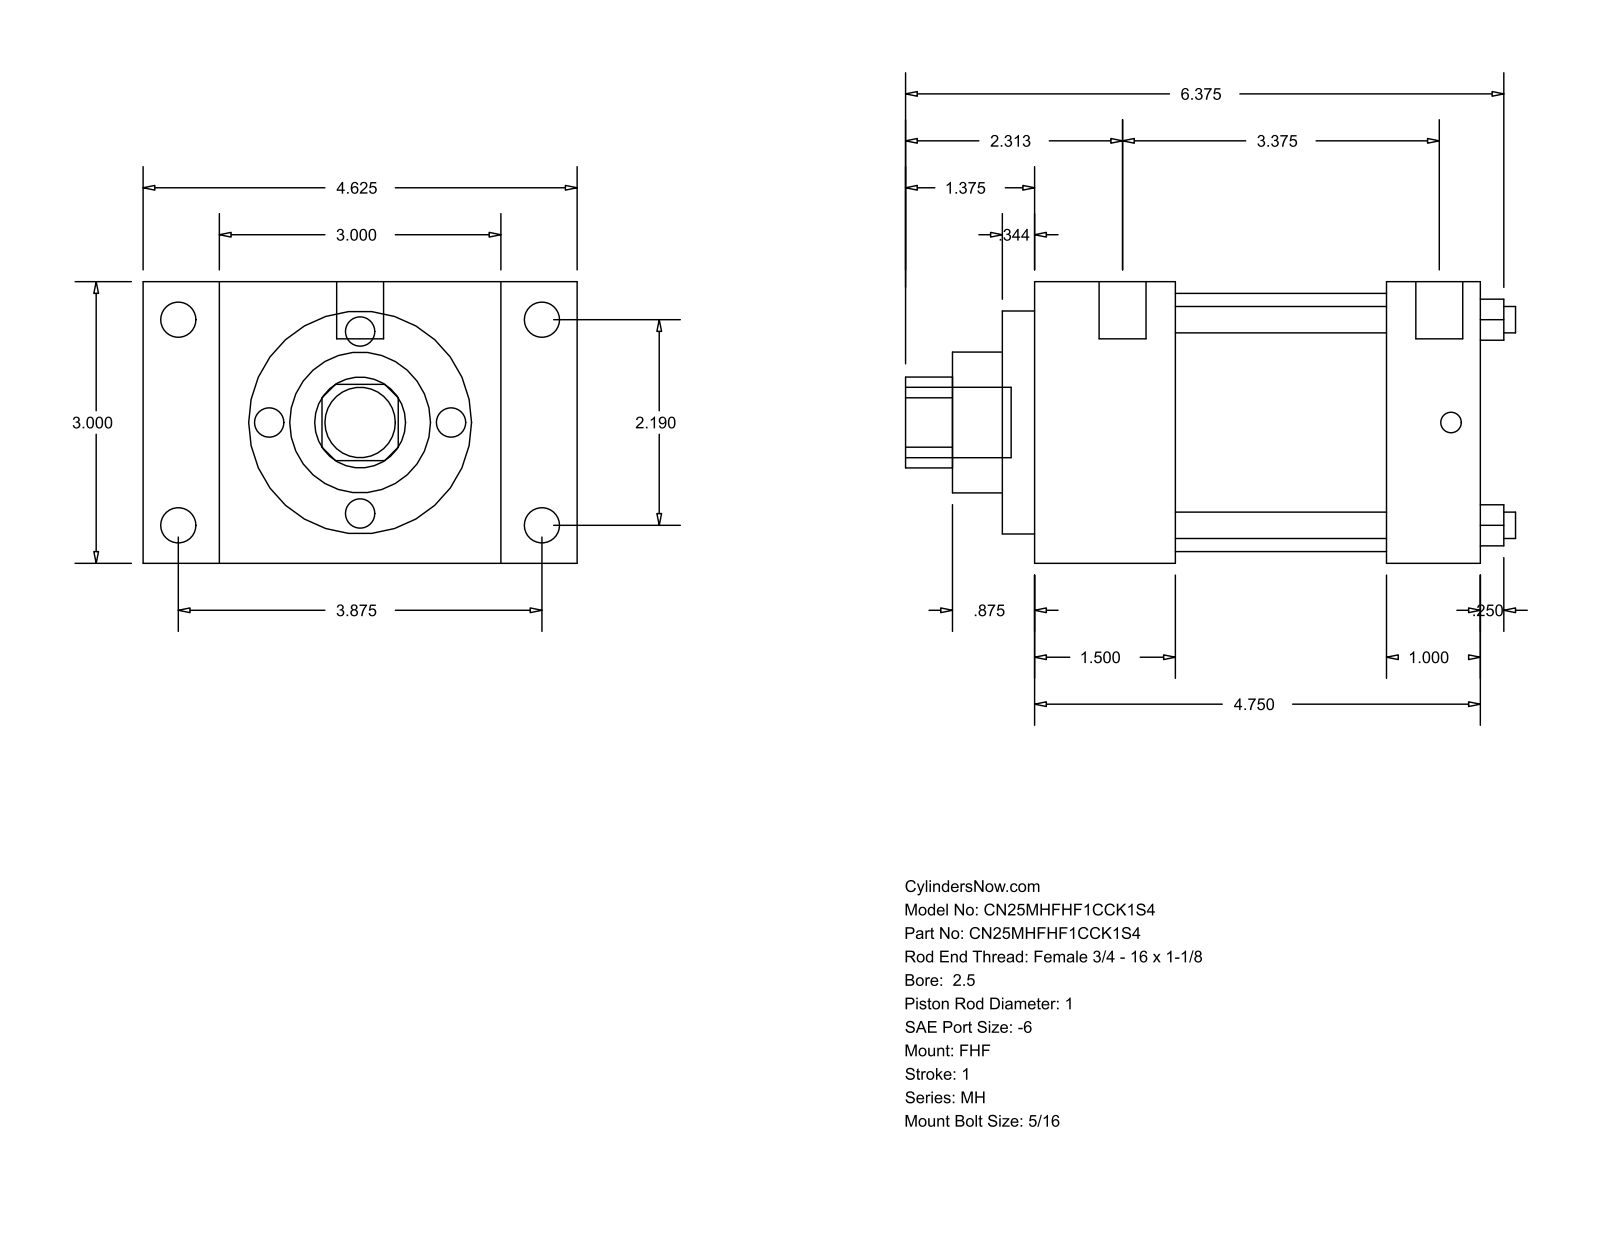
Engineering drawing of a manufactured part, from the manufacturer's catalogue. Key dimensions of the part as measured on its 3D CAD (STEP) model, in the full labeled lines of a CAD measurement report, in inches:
Part name (STEP PRODUCT): MH_FHF__0250_1
STEP written by: GSSL Pune (CONFIG_CONTROL_DESIGN)
Units: inches
Bodies: 0 solids, 90 faces (61 planar, 29 cylindrical, 0 other)
Overall size (bounding box): 6.5 × 4.625 × 3
Round holes (diameter × count): ⌀0.281 ×4, ⌀1 ×1, ⌀1.5 ×1, ⌀2.375 ×1, ⌀2.75 ×1
Round bosses / shafts (diameter × count): ⌀0.375 ×4, ⌀0.219 ×4, ⌀0.5 ×2, ⌀0.75 ×1
Partial cylindrical surfaces — rounded edges, fillets, slot ends (radius × count): R0.484 ×1
Main face-to-face distances: 3, 4.75, 1.5, 3.25, 0.813, 3.813, 4.625, 1, 3.75, 2.25
Hole centre spacings: 1.548, 2.19, 3.097
